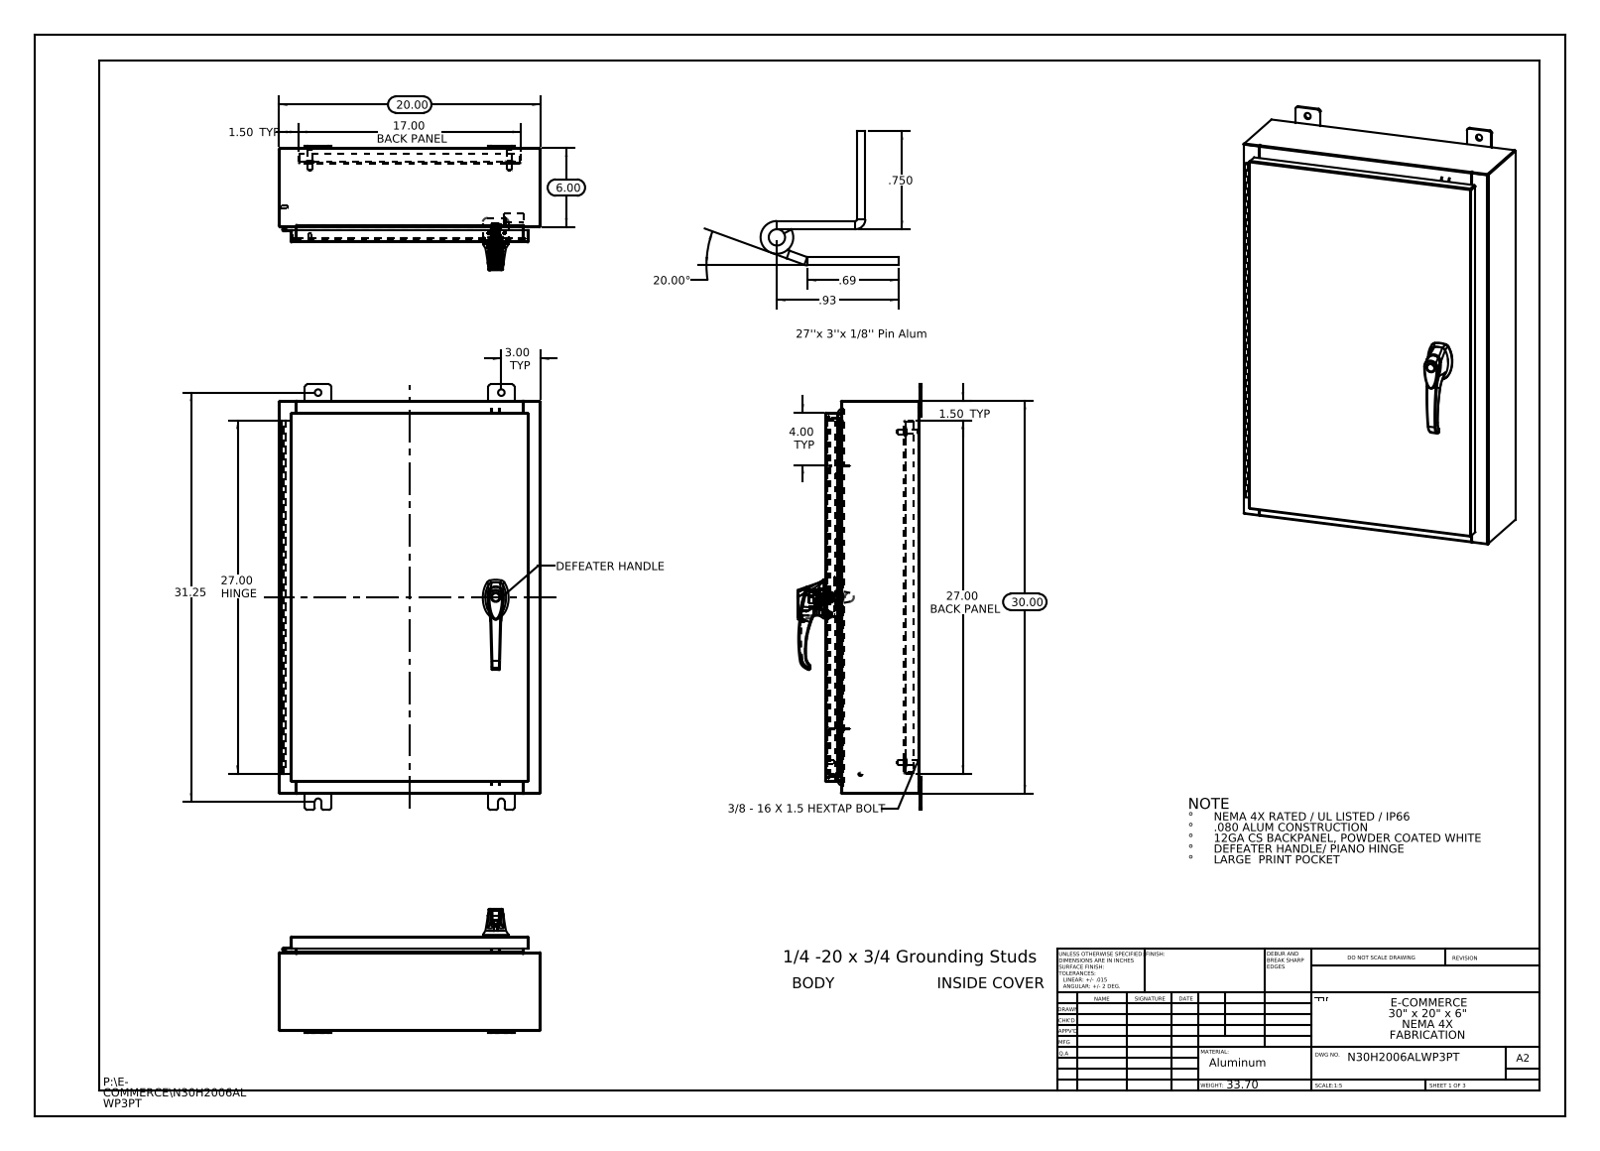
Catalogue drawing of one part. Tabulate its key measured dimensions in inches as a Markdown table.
| quantity | value |
| --- | --- |
| part name | N30H2006ALWP3PT Defeater Handle Rod; N30H2006ALWP3PT Mounting Feet; Quarter-20 CD Stud; 2616310101 (+8 more) |
| STEP written by | SolidWorks 2013 (CONFIG_CONTROL_DESIGN) |
| units | inches |
| bodies | 37 solids, 2662 faces (971 planar, 993 cylindrical, 698 other) |
| overall size | 32.5 × 20 × 9.495 |
| volume | 221.6 in³ |
| surface area | 5 445 in² |
| round holes (diameter × count) | 0.5 × 8, 0.25 × 4, 0.138 × 3, 0.161 × 3, 0.079 × 2, 0.203 × 2, 0.313 × 2, 0.437 × 2, 0.125 × 1, 0.125 × 1, 0.197 × 1, 0.276 × 1 |
| round bosses / shafts (diameter × count) | 0.625 × 4, 0.375 × 4, 0.33 × 4, 0.157 × 4, 0.14 × 4, 0.315 × 3, 0.236 × 3, 1.181 × 1 |
| partial cylindrical surfaces (radius × count) | 0.118 × 37, 0.006 × 33, 0.013 × 24, 0.19 × 24, 0.088 × 18, 0.039 × 15, 0.028 × 12, 0.008 × 6 |
| main face-to-face distances | 0.075, 7.126, 0.104, 7.051, 7.201, 1, 1.075, 6.051, 6.126, 1.179 |
| hole center spacings | 8.369, 15.143, 0.295, 0.625, 0.841, 1.25, 1.313, 1.561 |
